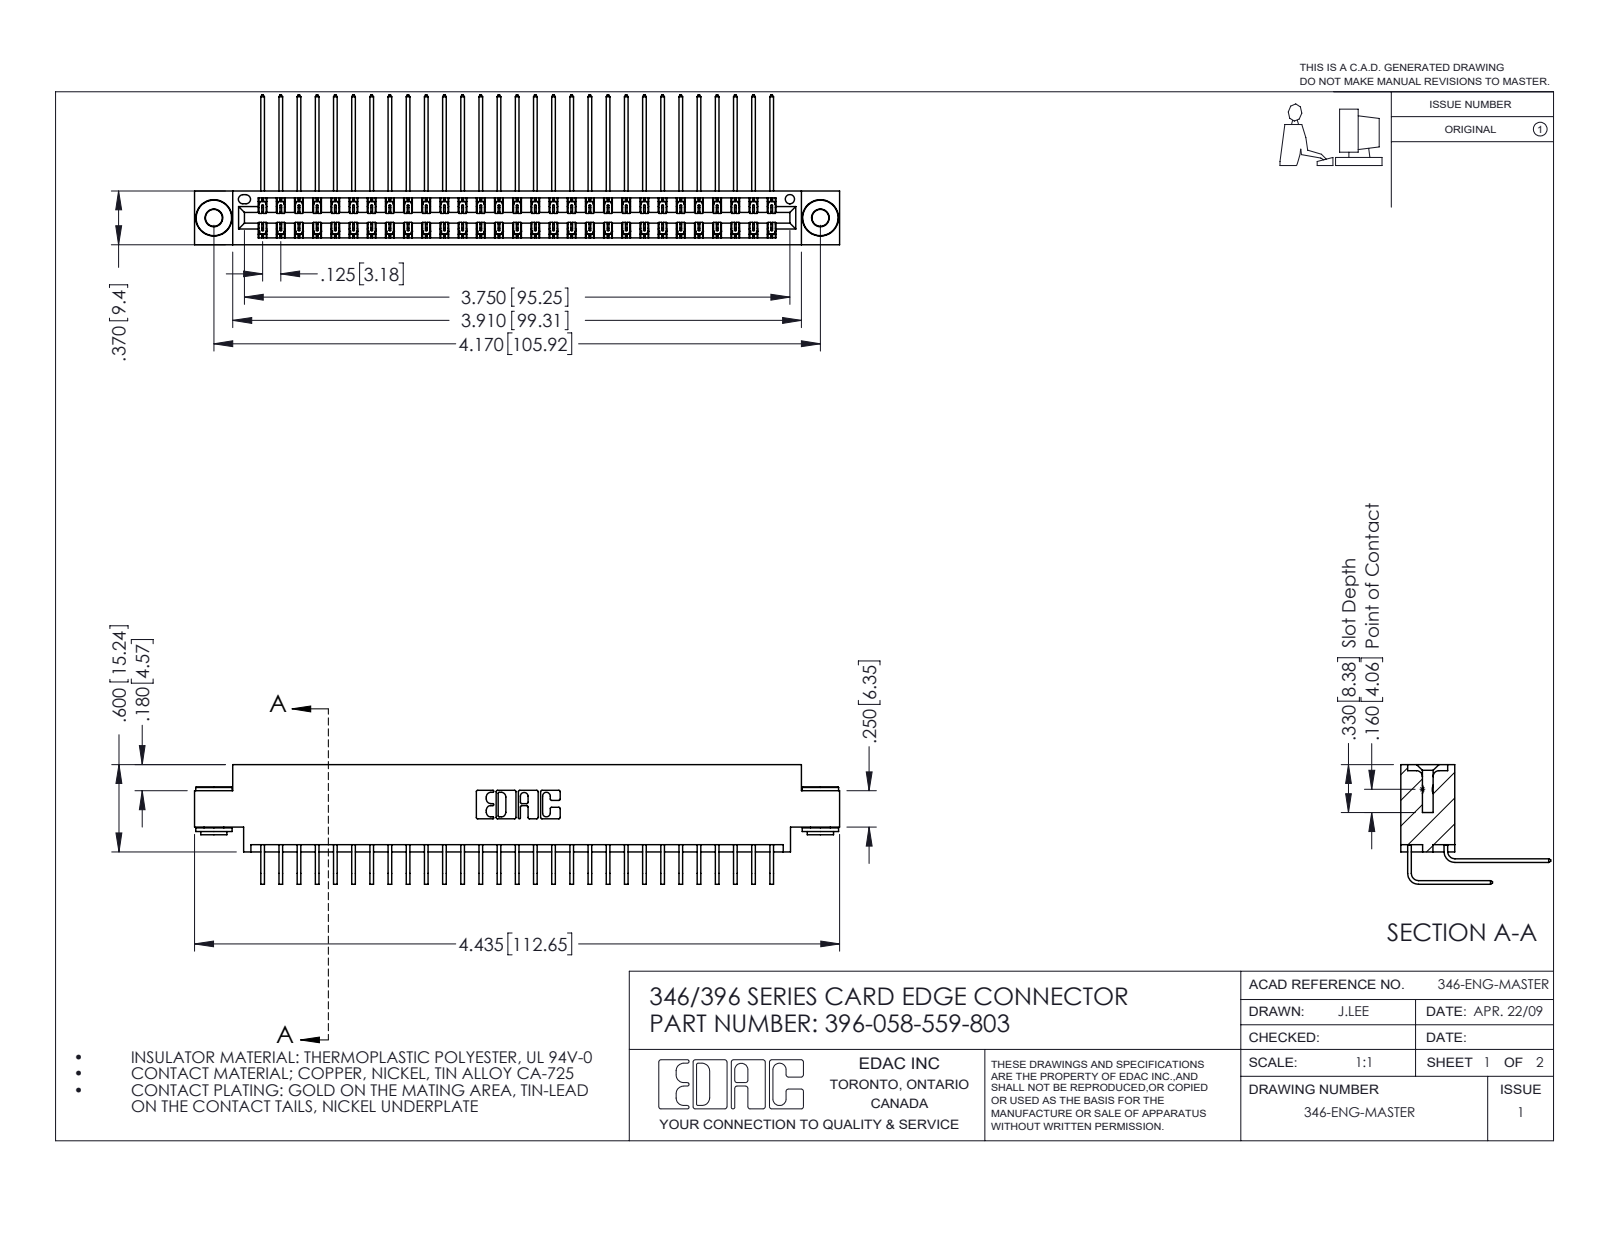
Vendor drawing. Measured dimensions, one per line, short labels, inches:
name: 396-058-559-803; 345-250-002_345-250-002-102; 345-292-001_558 559 Tail - 1; 346 Part_0.170 Offset - 0.156 Dia-TH (+1 more)
written by: SolidWorks 2016 (CONFIG_CONTROL_DESIGN)
unit: in
bodies: 61 solids, 3296 faces (2236 planar, 1052 cylindrical, 8 other)
size: 4.435 × 1.03 × 0.823
volume: 0.676 in³; area: 26.4 in²
holes: 2× ⌀0.116, 2× ⌀0.156, 1× ⌀0.064
bosses: 2× ⌀0.25, 2× ⌀0.18, 2× ⌀0.136
rounds: 87× R0.006, 22× R0.01, 6× R0.007, 6× R0.031, 3× R0.026, 2× R0.014, 2× R0.022, 2× R0.024
face distances: 0.048, 0.322, 0.025, 0.37, 0.25, 0.072, 0.298, 0.275, 0.15, 0.148
hole spacings: 0.246, 3.962, 4.17
